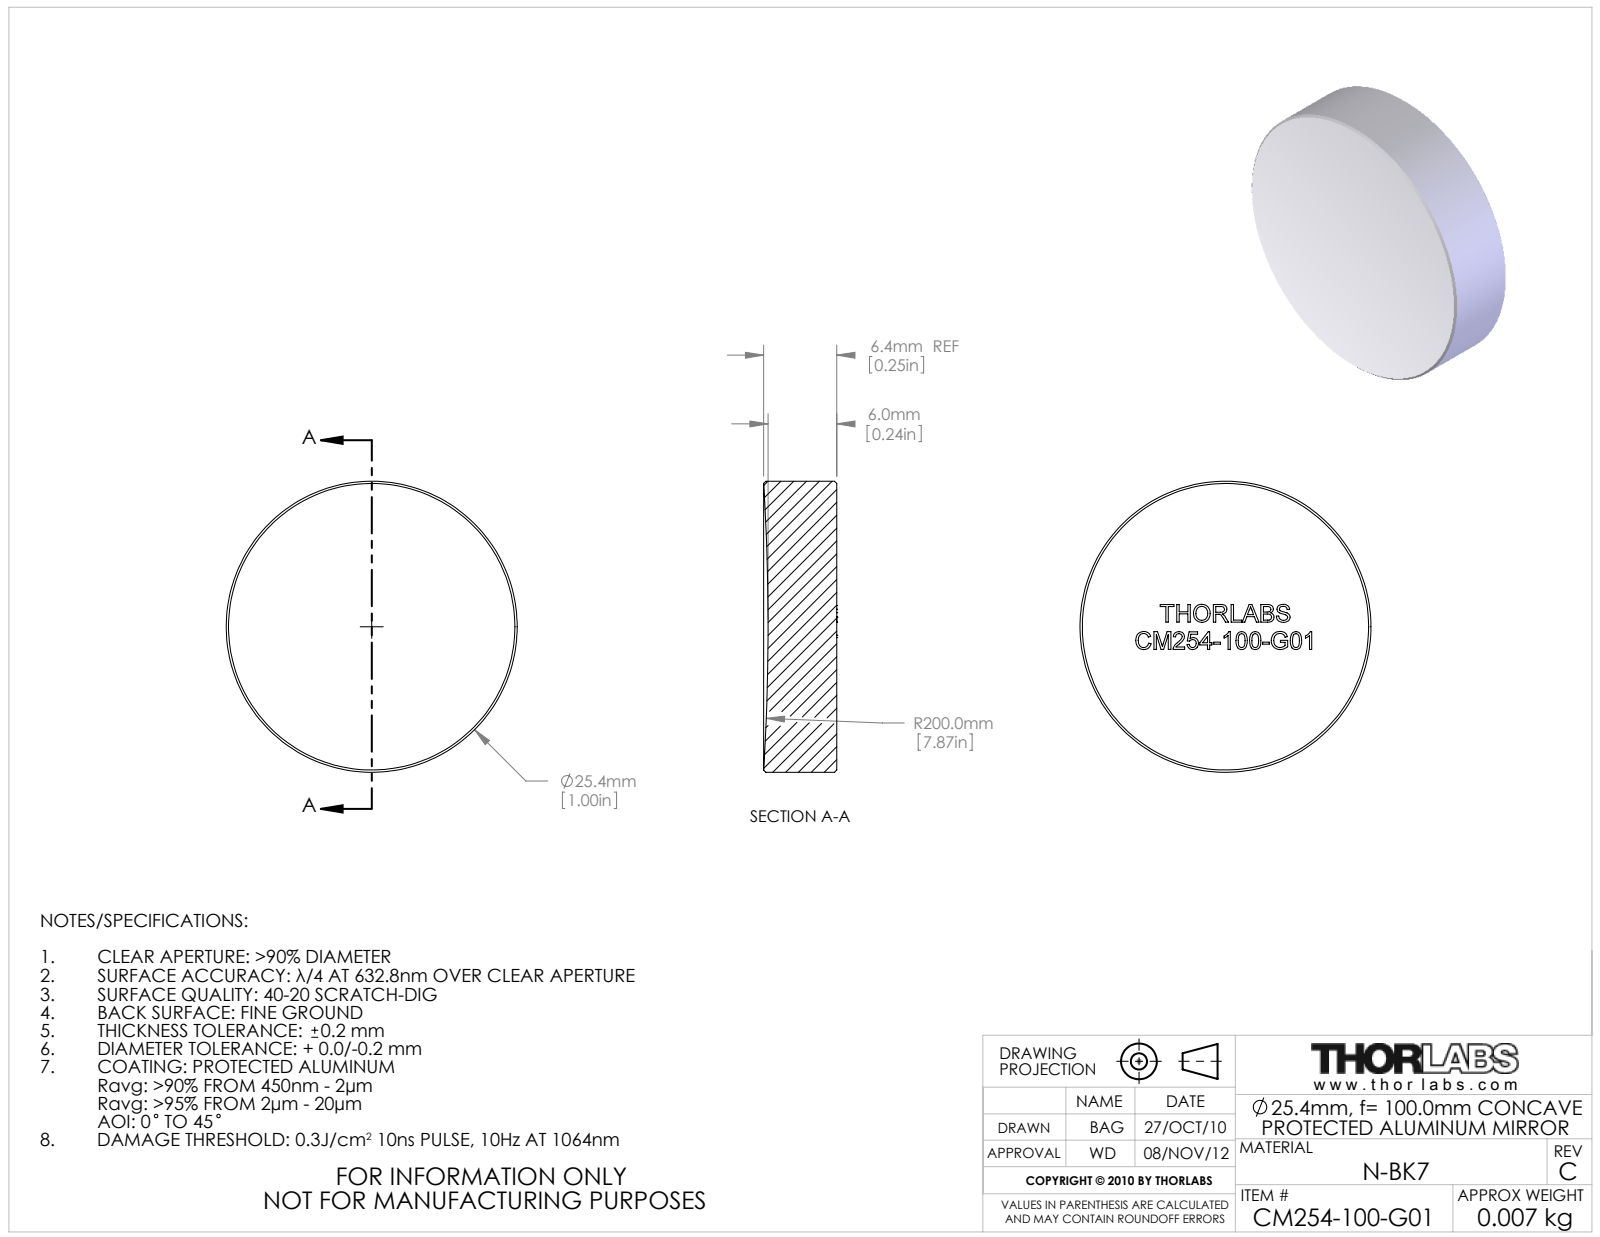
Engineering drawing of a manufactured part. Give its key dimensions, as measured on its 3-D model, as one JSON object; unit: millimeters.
{"part_name": "12012-E0W", "step_written_by": "SolidWorks 2009 (AUTOMOTIVE_DESIGN)", "units": "millimeters", "bodies": {"solids": 1, "faces": 275, "planar": 154, "cylindrical": 2, "other": 119}, "overall_size": [25.4, 25.4, 6.4], "volume_mm3": 3150, "surface_area_mm2": 1505, "round_bosses_or_shafts": [[25.4, 1]], "face_to_face_distances": [1.9, 1.5, 1.7, 4.1, 0.7, 1.5, 0.9, 3.9, 2.7, 3.7]}
